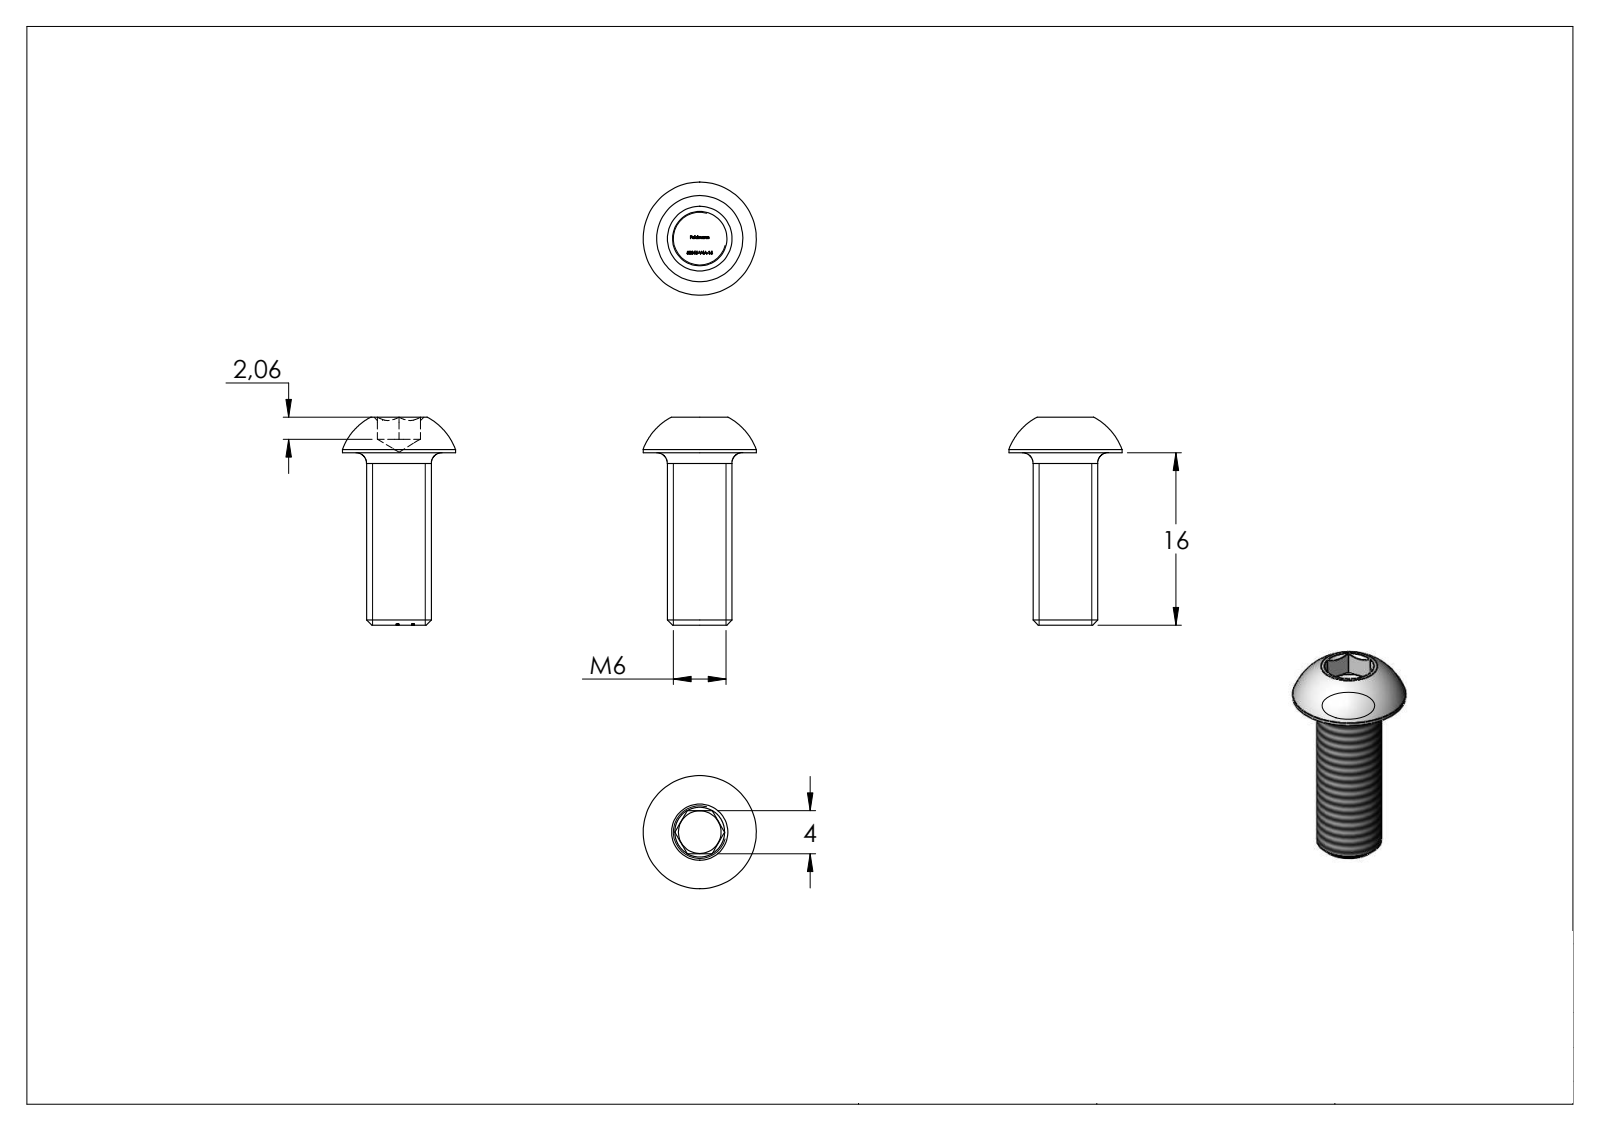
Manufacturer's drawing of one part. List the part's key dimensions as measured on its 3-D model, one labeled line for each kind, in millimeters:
Part name (STEP PRODUCT): 58346-V4A-16
STEP written by: SolidWorks 2015 (CONFIG_CONTROL_DESIGN)
Units: millimetres
Bodies: 1 solid, 284 faces (167 planar, 2 cylindrical, 115 other)
Overall size (bounding box): 21.3 × 10.5 × 10.5
Volume: 623 mm³ · Surface area: 543 mm²
Round bosses / shafts (diameter × count): ⌀10.5 ×1, ⌀6 ×1
Main face-to-face distances: 16, 4, 3.3, 19.3, 1.24, 2.06, 17.24, 19.2, 17.14, 15.9
